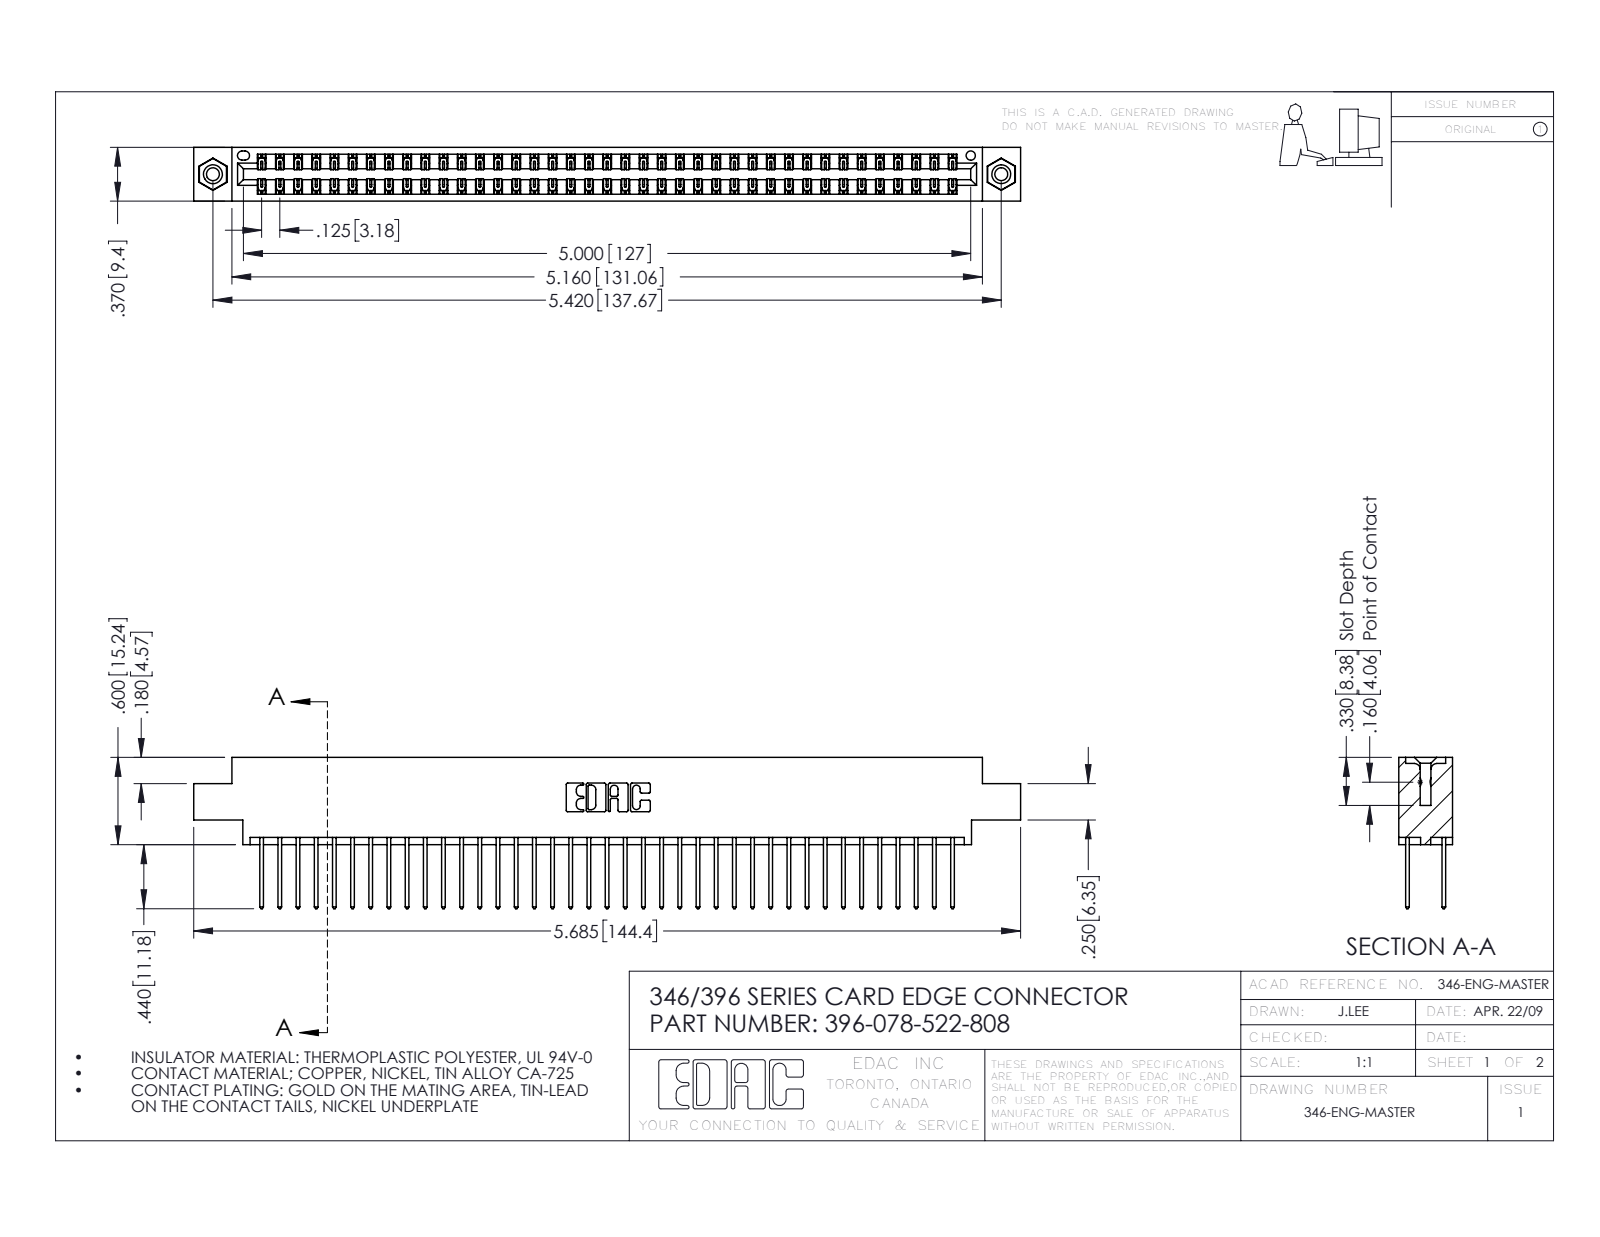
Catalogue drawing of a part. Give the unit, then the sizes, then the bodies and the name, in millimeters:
Units: millimetres
Overall size (bounding box): 144.4 × 26.4 × 9.4
Round holes (diameter × count): ⌀2.3 ×2, ⌀3.2 ×2, ⌀4 ×2, ⌀1.6 ×1
Round bosses / shafts (diameter × count): ⌀3.9 ×2
Partial cylindrical surfaces — rounded edges, fillets, slot ends (radius × count): R0.2 ×117, R0.3 ×78, R0.3 ×22, R0.2 ×6, R0.8 ×6, R0.7 ×3, R0.4 ×2, R0.6 ×2
Main face-to-face distances: 1.2, 8.2, 6.4, 9.4, 1.8, 7.6, 0.6, 7, 5.6, 3.8
Hole centre spacings: 6.2, 132.4, 137.7
Volume: 14 100 mm³ · Surface area: 20 460 mm²
Bodies: 81 solids, 4242 faces (2842 planar, 1384 cylindrical, 16 other)
Part name (STEP PRODUCT): 345-250-001_345-250-003-102; 345-292-001_345-293-122; 346 Part_0.170 Offset - 0.156 Dia-TI; 396-078-522-808
STEP written by: SolidWorks 2016 (CONFIG_CONTROL_DESIGN)
